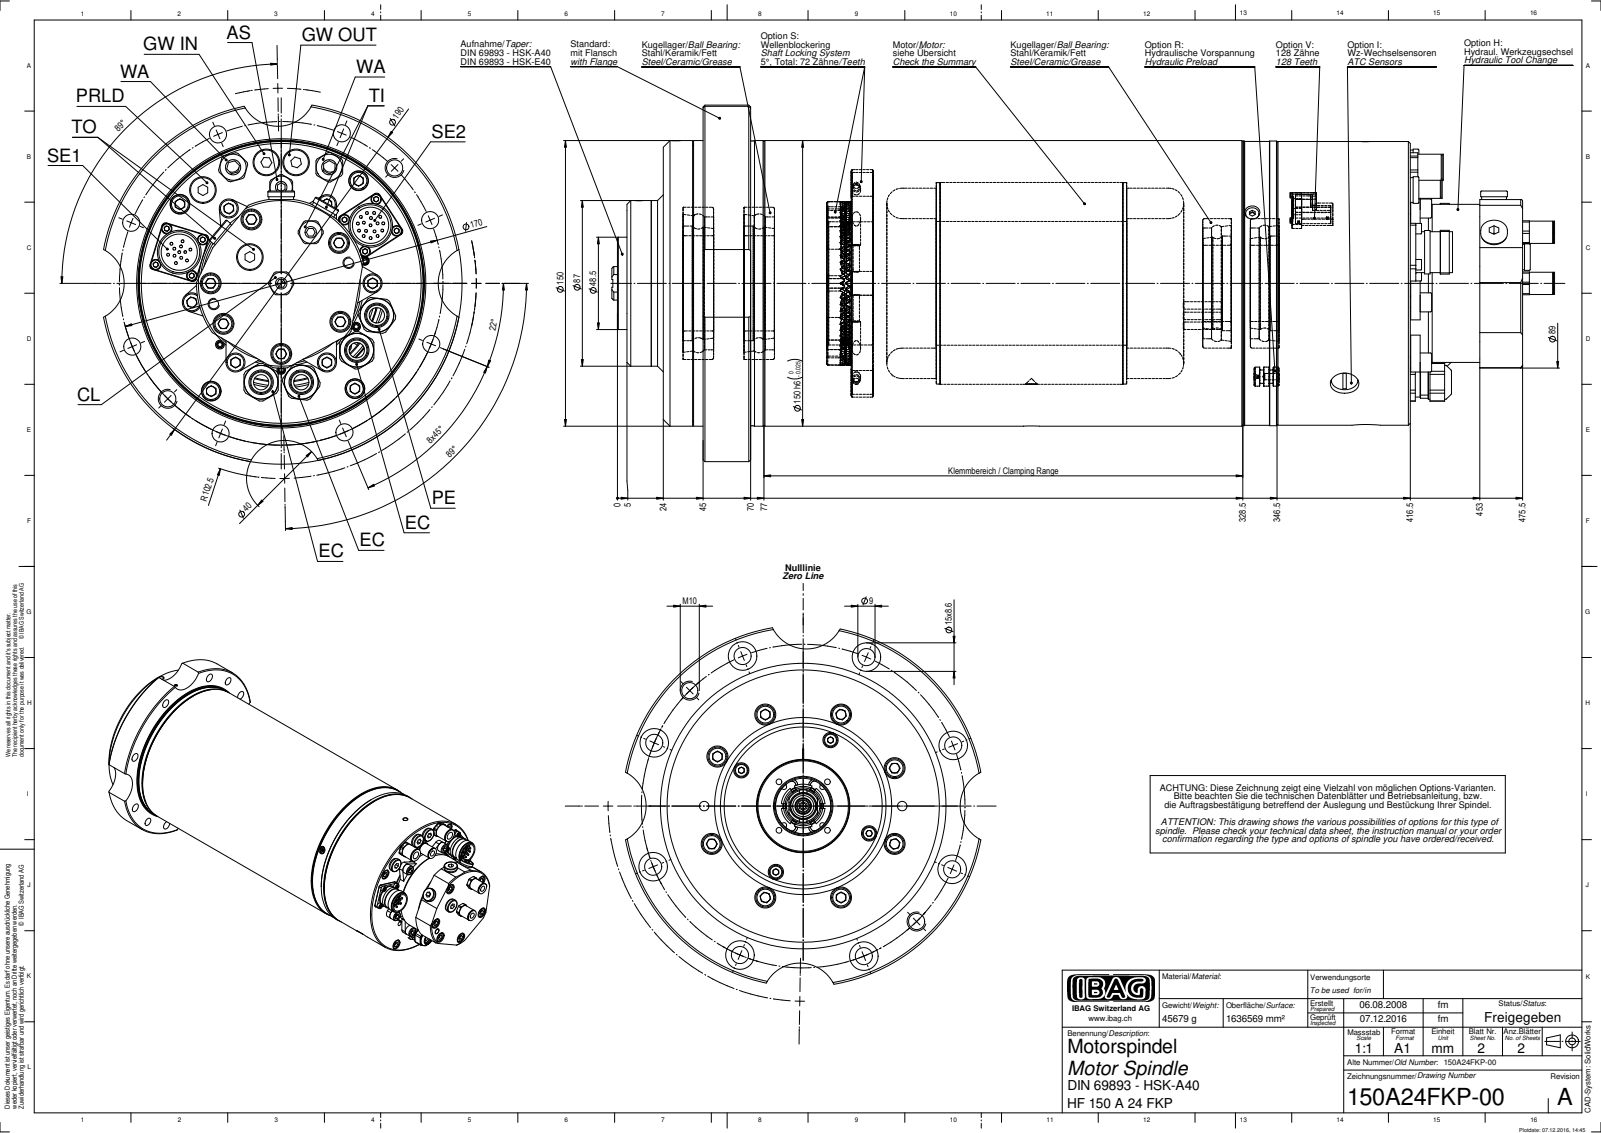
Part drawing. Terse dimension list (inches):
name: 150A24FKP-00A
written by: SolidWorks 2010 (CONFIG_CONTROL_DESIGN)
unit: in
bodies: 0 solids, 1296 faces (549 planar, 486 cylindrical, 261 other)
size: 21.789 × 7.426 × 7.414
holes: 14× ⌀0.433, 12× ⌀0.315, 12× ⌀0.591, 8× ⌀0.354, 4× ⌀0.409, 4× ⌀0.421, 4× ⌀0.638, 3× ⌀0.236, 2× ⌀0.177, 2× ⌀0.335, 2× ⌀0.748, 1× ⌀0.138
bosses: 29× ⌀0.059, 8× ⌀0.394, 8× ⌀0.217, 7× ⌀0.551, 5× ⌀0.512, 4× ⌀0.701, 4× ⌀0.661, 4× ⌀0.614
rounds: 12× R0.039, 4× R0.177, 4× R0.39, 3× R0.26, 2× R0.305, 2× R0.787, 1× R0.571, 1× R1.565
face distances: 13.642, 0.984, 0.831, 1.815, 15.457, 14.626, 11.992, 11.161, 10.177, 3.465
hole spacings: 3.346, 2.047, 2.37, 2.406, 3.907, 3.938, 4.999, 5.016
